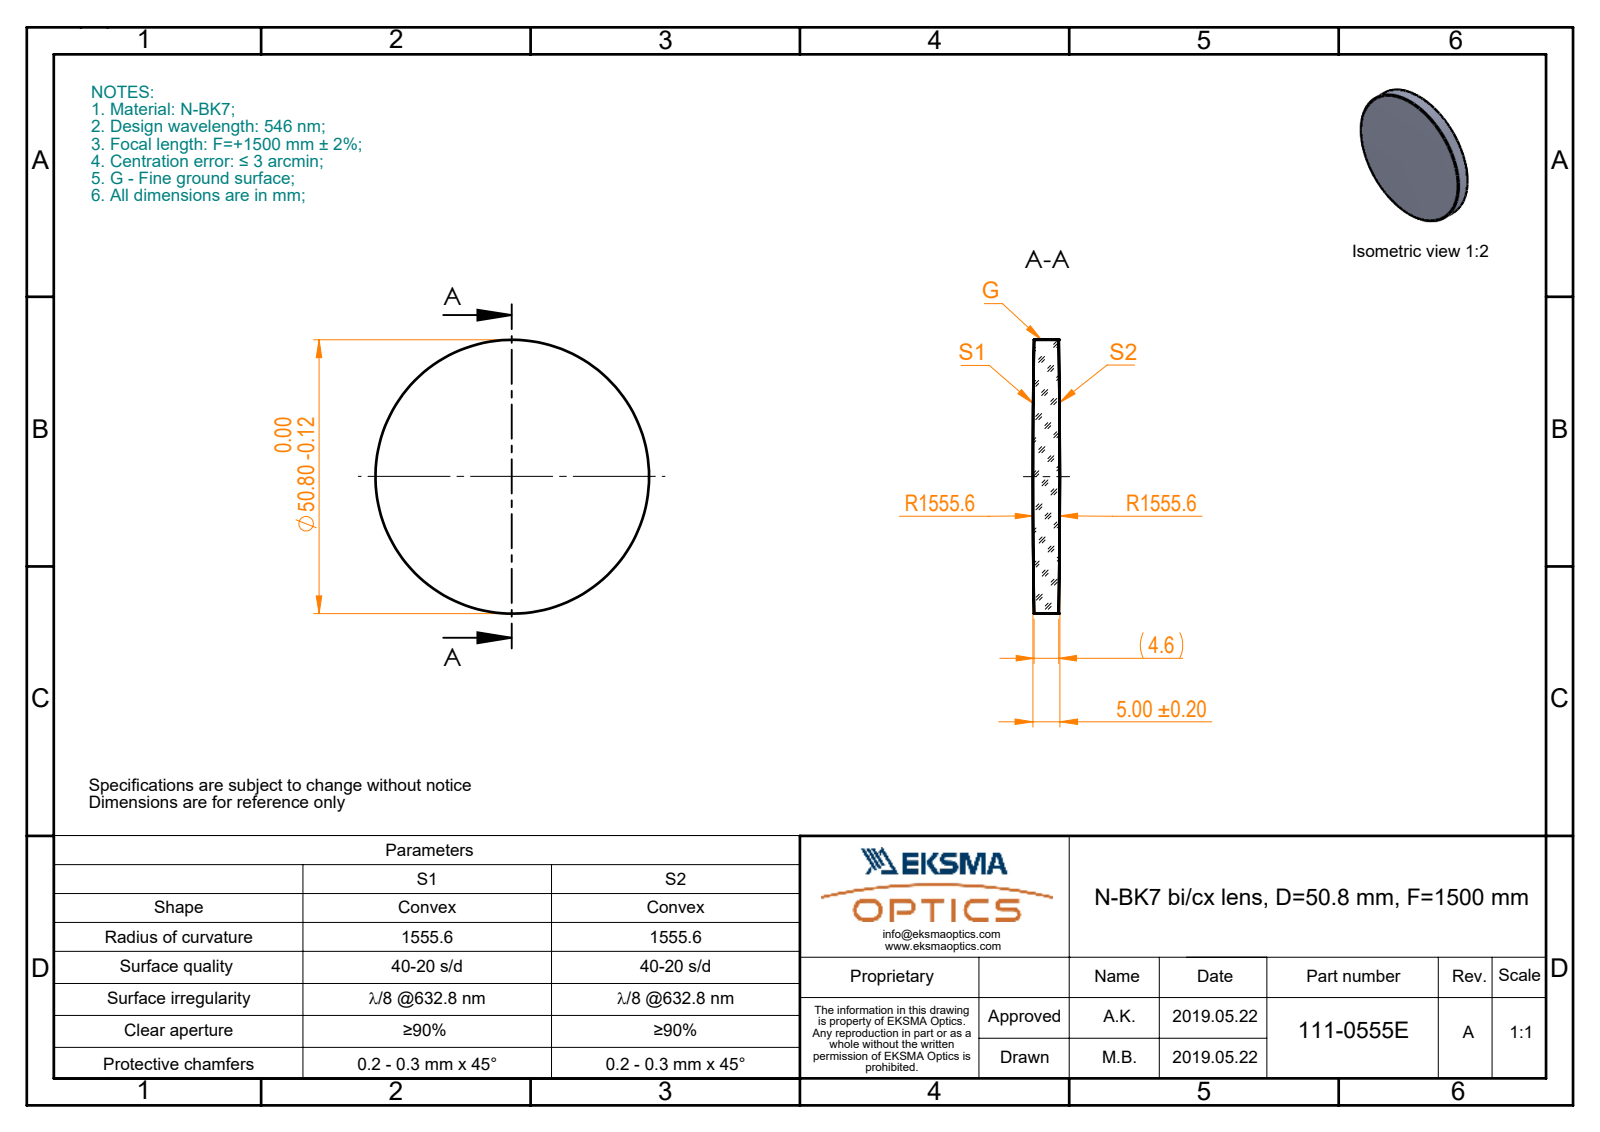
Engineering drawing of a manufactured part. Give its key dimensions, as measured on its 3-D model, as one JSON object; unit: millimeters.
{"part_name": "111-0555E BK7 bi-cx 50.8 F1500", "step_written_by": "SolidWorks 2019 (CONFIG_CONTROL_DESIGN)", "units": "millimeters", "bodies": {"solids": 1, "faces": 6, "planar": 0, "cylindrical": 2, "other": 4}, "overall_size": [50.8, 50.8, 5], "volume_mm3": 9714, "surface_area_mm2": 4786, "round_bosses_or_shafts": [[50.8, 1]]}
